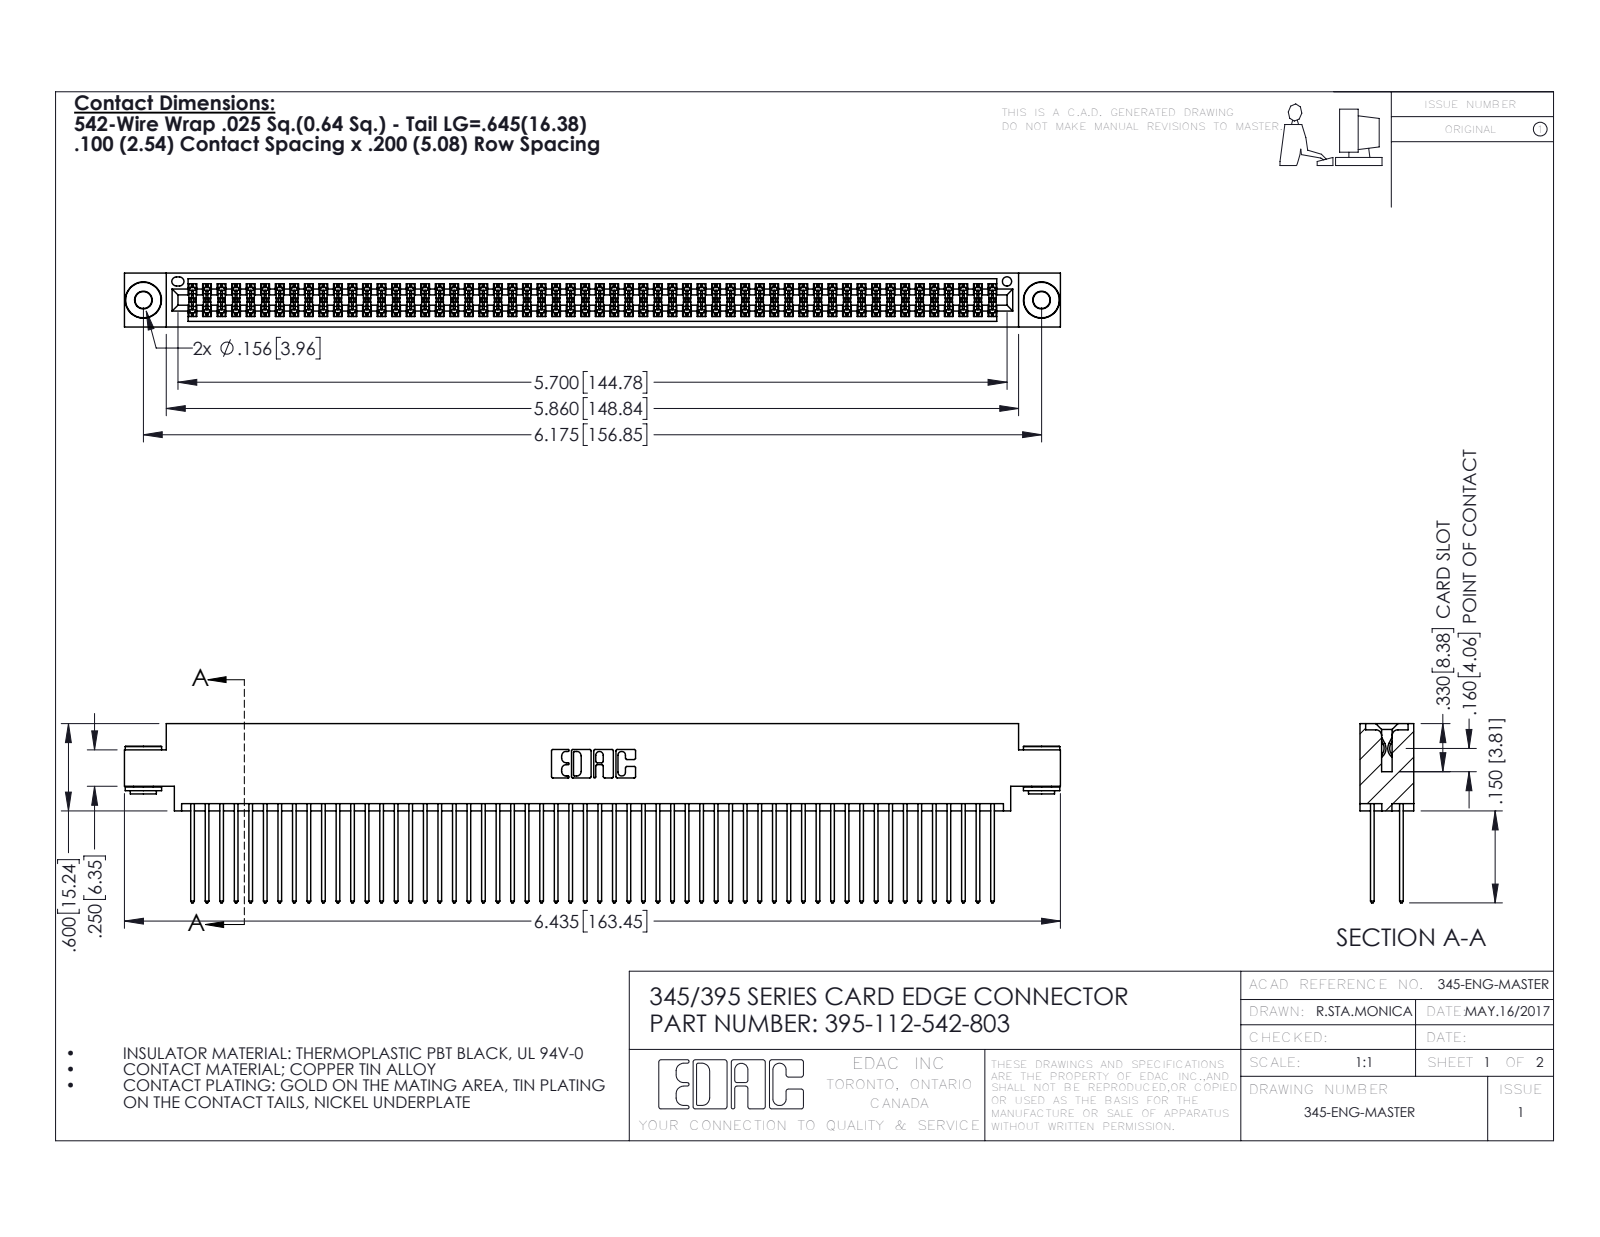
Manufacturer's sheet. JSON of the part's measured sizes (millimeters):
{"part_name": "345-292-001_345-293-142; 395-112-542-803; 345 Part_0.170 Offset - 0.156 Dia-TH; 345-250-002_345-250-002-102", "step_written_by": "SolidWorks 2016 (CONFIG_CONTROL_DESIGN)", "units": "millimeters", "bodies": {"solids": 115, "faces": 5768, "planar": 3790, "cylindrical": 1970, "other": 8}, "overall_size": [163.4, 31.3, 9.4], "volume_mm3": 16440, "surface_area_mm2": 27350, "round_holes": [[2.9, 2], [4, 2], [1.6, 1]], "round_bosses_or_shafts": [[6.4, 2], [4.6, 2], [3.5, 2]], "partial_cylinders_radius": [[0.2, 168], [0.3, 112], [0.3, 22], [0.2, 6], [0.8, 6], [0.7, 3], [0.4, 2], [0.5, 2]], "face_to_face_distances": [1.8, 7.6, 5.1, 2.5, 6.9, 0.6, 9.4, 5.7, 4.4, 3.8], "hole_center_spacings": [6.9, 150.9, 156.8]}
